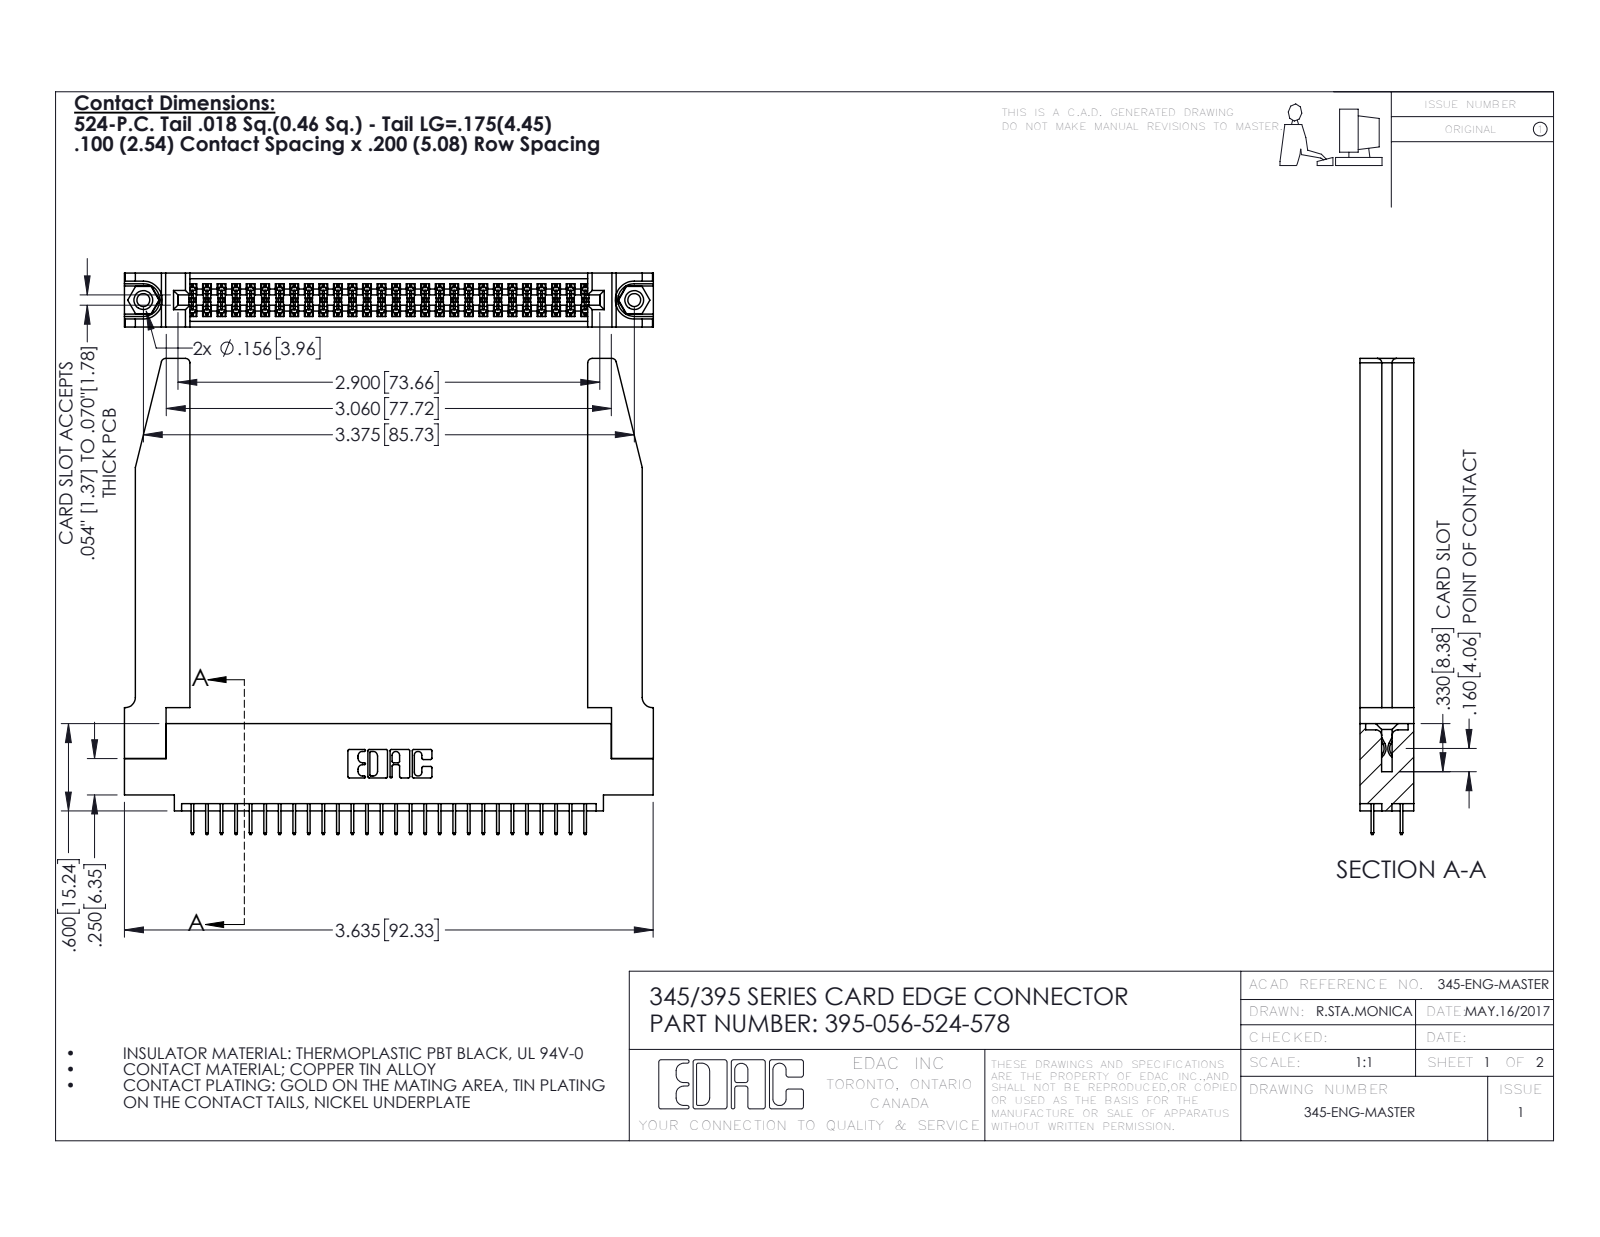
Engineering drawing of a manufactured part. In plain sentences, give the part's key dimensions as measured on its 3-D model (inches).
The part is named "395-056-524-578; 345-220-078_345-220-078; 345-250-001_345-250-001-102; 345 Part_0.110 Offset - 0.156 Dia-TH (+1 more)". Its 3-D file was written by "SolidWorks 2016 (CONFIG_CONTROL_DESIGN)". It is 61 solids with 3388 faces: 2410 planar, 926 cylindrical and 52 other. Overall it measures 3.636 by 3.272 by 0.37 inches. Its volume is 1.004 cubic inches and its surface area 29.87 square inches. Round holes: 2 of diameter 0.089, 2 of diameter 0.125, 2 of diameter 0.156, 1 of diameter 0.064. Round bosses or shafts: 2 of diameter 0.155. Partial cylindrical surfaces (rounded edges, fillets, slot ends): 84 of radius 0.006, 22 of radius 0.01, 8 of radius 0.03, 6 of radius 0.007, 6 of radius 0.031, 3 of radius 0.026, 2 of radius 0.014, 2 of radius 0.019. The main face-to-face distances are 0.37, 0.072, 0.298, 0.098, 0.272, 0.025, 0.2, 0.225, 0.148, 0.15. The hole center spacings are 0.27, 3.14, 3.375.
